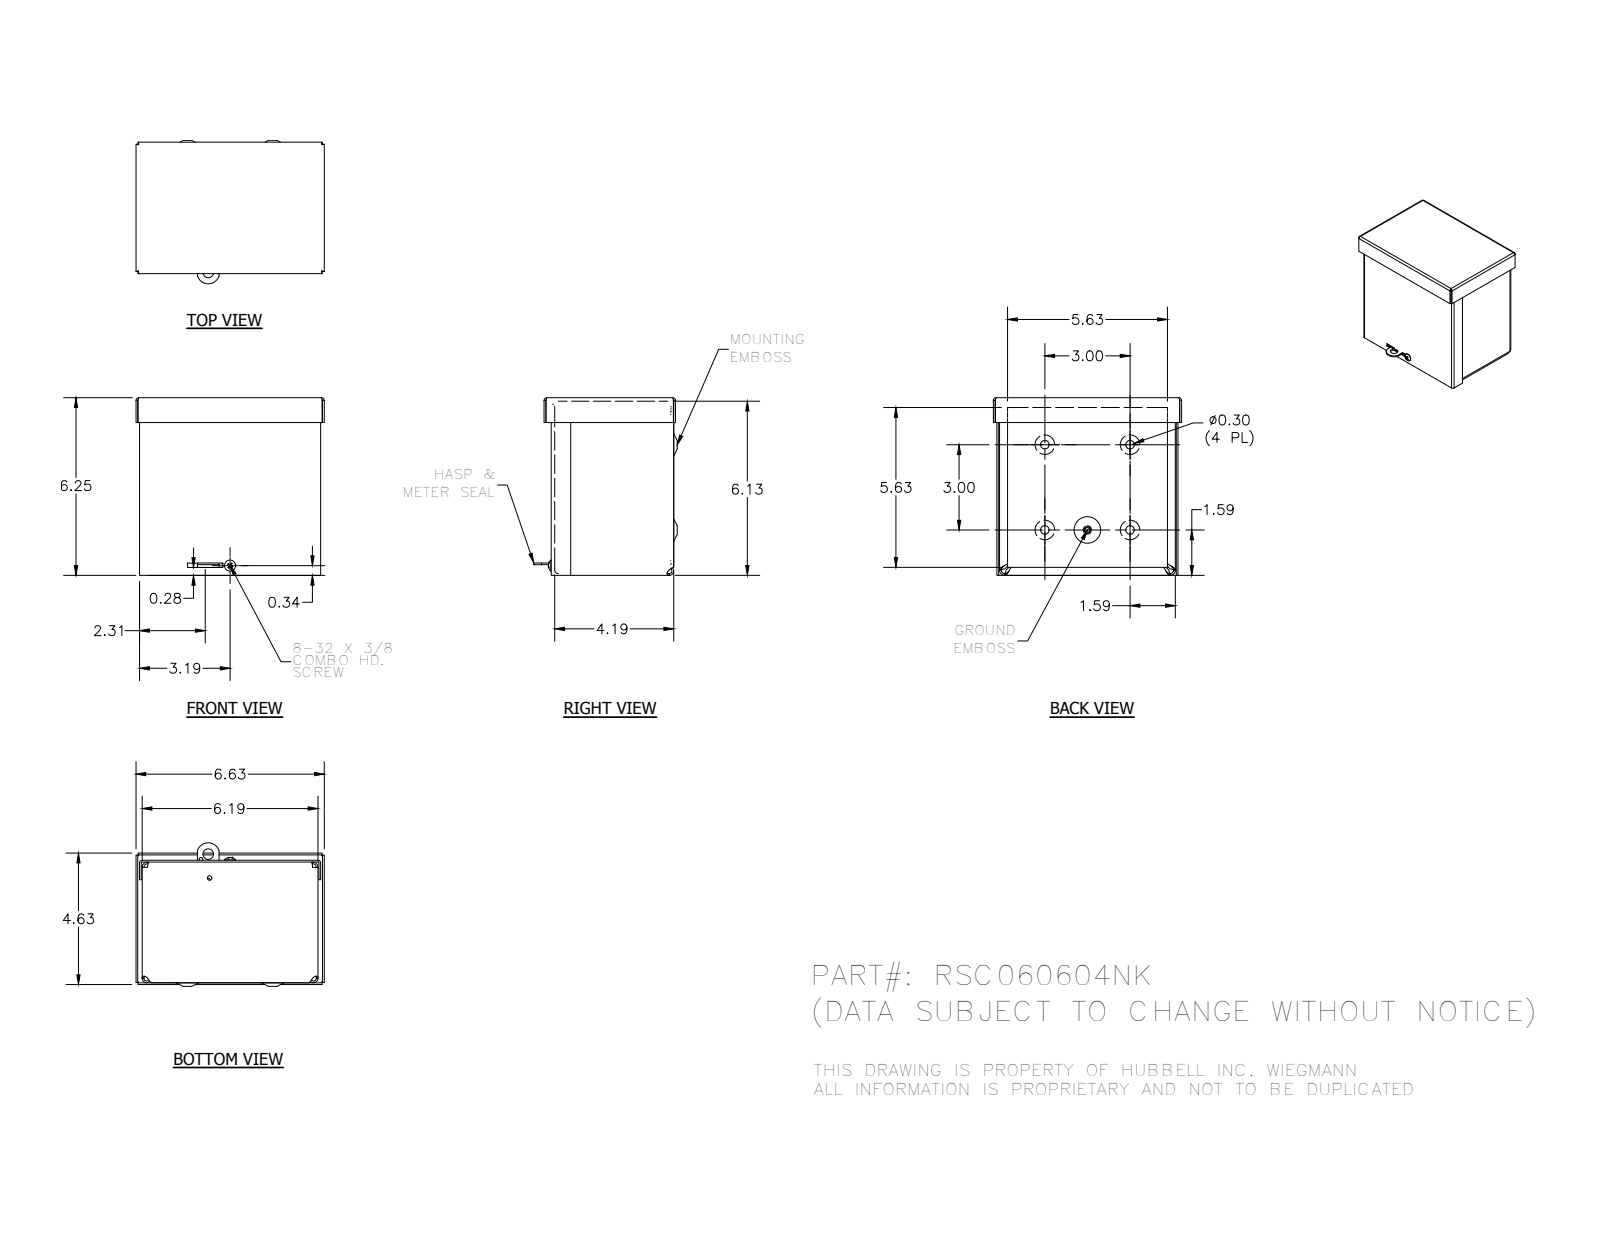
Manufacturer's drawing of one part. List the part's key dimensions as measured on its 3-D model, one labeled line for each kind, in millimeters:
Part name (STEP PRODUCT): RSC060604NK_WRAP; RSC0606NK_LID; RSC0604NK_CAP; 3183 (+3 more)
STEP written by: Autodesk Inventor 2014 (AUTOMOTIVE_DESIGN)
Units: millimetres
Bodies: 6 solids, 347 faces (153 planar, 73 cylindrical, 121 other)
Overall size (bounding box): 168.28 × 158.76 × 130.17
Volume: 263 067 mm³ · Surface area: 340 754 mm²
Round holes (diameter × count): ⌀7.62 ×4, ⌀7.95 ×2, ⌀3.17 ×1, ⌀3.45 ×1, ⌀3.76 ×1, ⌀3.96 ×1, ⌀4.19 ×1, ⌀9.52 ×1
Round bosses / shafts (diameter × count): ⌀9.75 ×1, ⌀5.8 ×1, ⌀4.17 ×1
Partial cylindrical surfaces — rounded edges, fillets, slot ends (radius × count): R0.79 ×8, R2.37 ×8, R3.17 ×8, R4.75 ×8, R1.4 ×4, R1.57 ×4, R2.38 ×4, R2.97 ×4
Main face-to-face distances: 1.58, 155.59, 1.57, 107.93, 157.17, 3.15, 106.35, 1.59, 109.52, 107.94
Hole centre spacings: 76.2, 38.1, 85.19, 107.76, 7.92, 19.73, 23.19, 31.79
